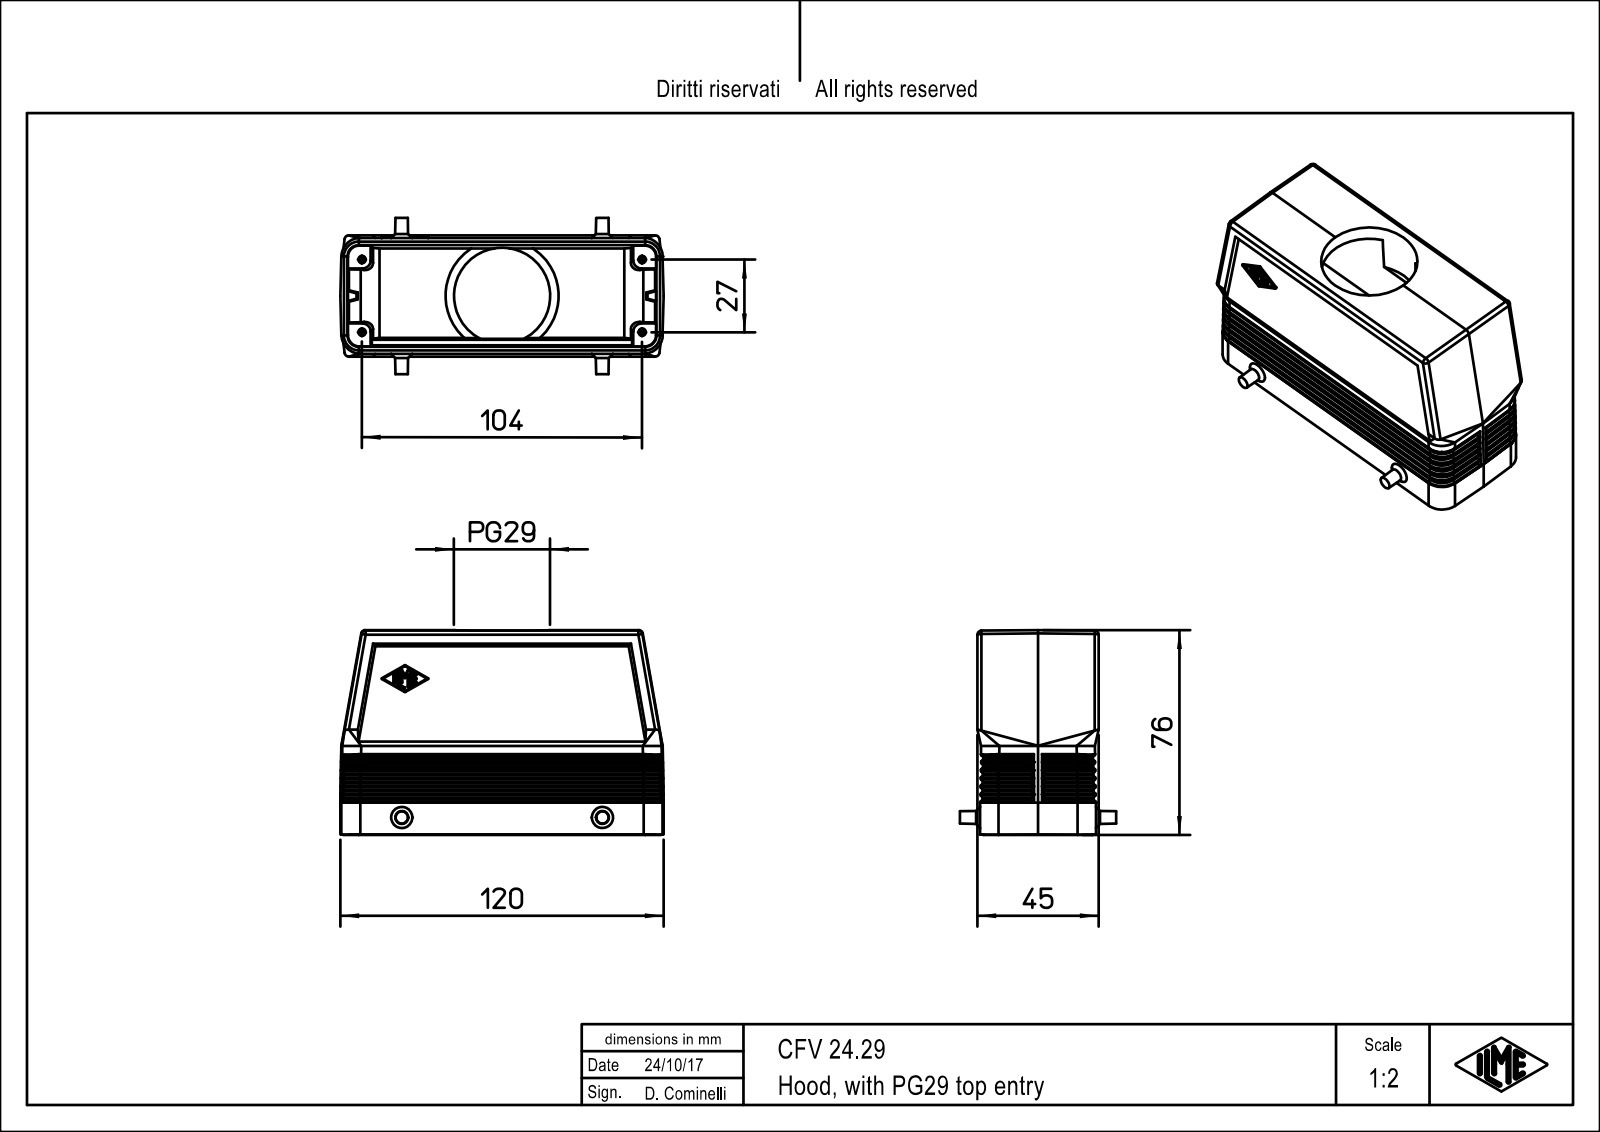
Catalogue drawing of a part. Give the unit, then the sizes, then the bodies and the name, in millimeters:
Units: millimetres
Overall size (bounding box): 120 × 76 × 58
Round holes (diameter × count): ⌀35.7 ×1
Partial cylindrical surfaces — rounded edges, fillets, slot ends (radius × count): R0.5 ×78, R0.33 ×15, R1.5 ×10, R7 ×8, R3 ×4, R4.2 ×4, R0.17 ×3, R0.67 ×1
Main face-to-face distances: 43, 2.01, 2, 4, 44, 1, 8.45, 6, 6.01, 4.01
Volume: 104 993 mm³ · Surface area: 53 686 mm²
Bodies: 1 solid, 527 faces (240 planar, 135 cylindrical, 152 other)
Part name (STEP PRODUCT): CFV_24.29
STEP written by: PTC Creo Elements/Direct Modeling 19.0E 27-Jun-2016 (C) Parametric Technology GmbH (AUTOMOTIVE_DESIGN)
